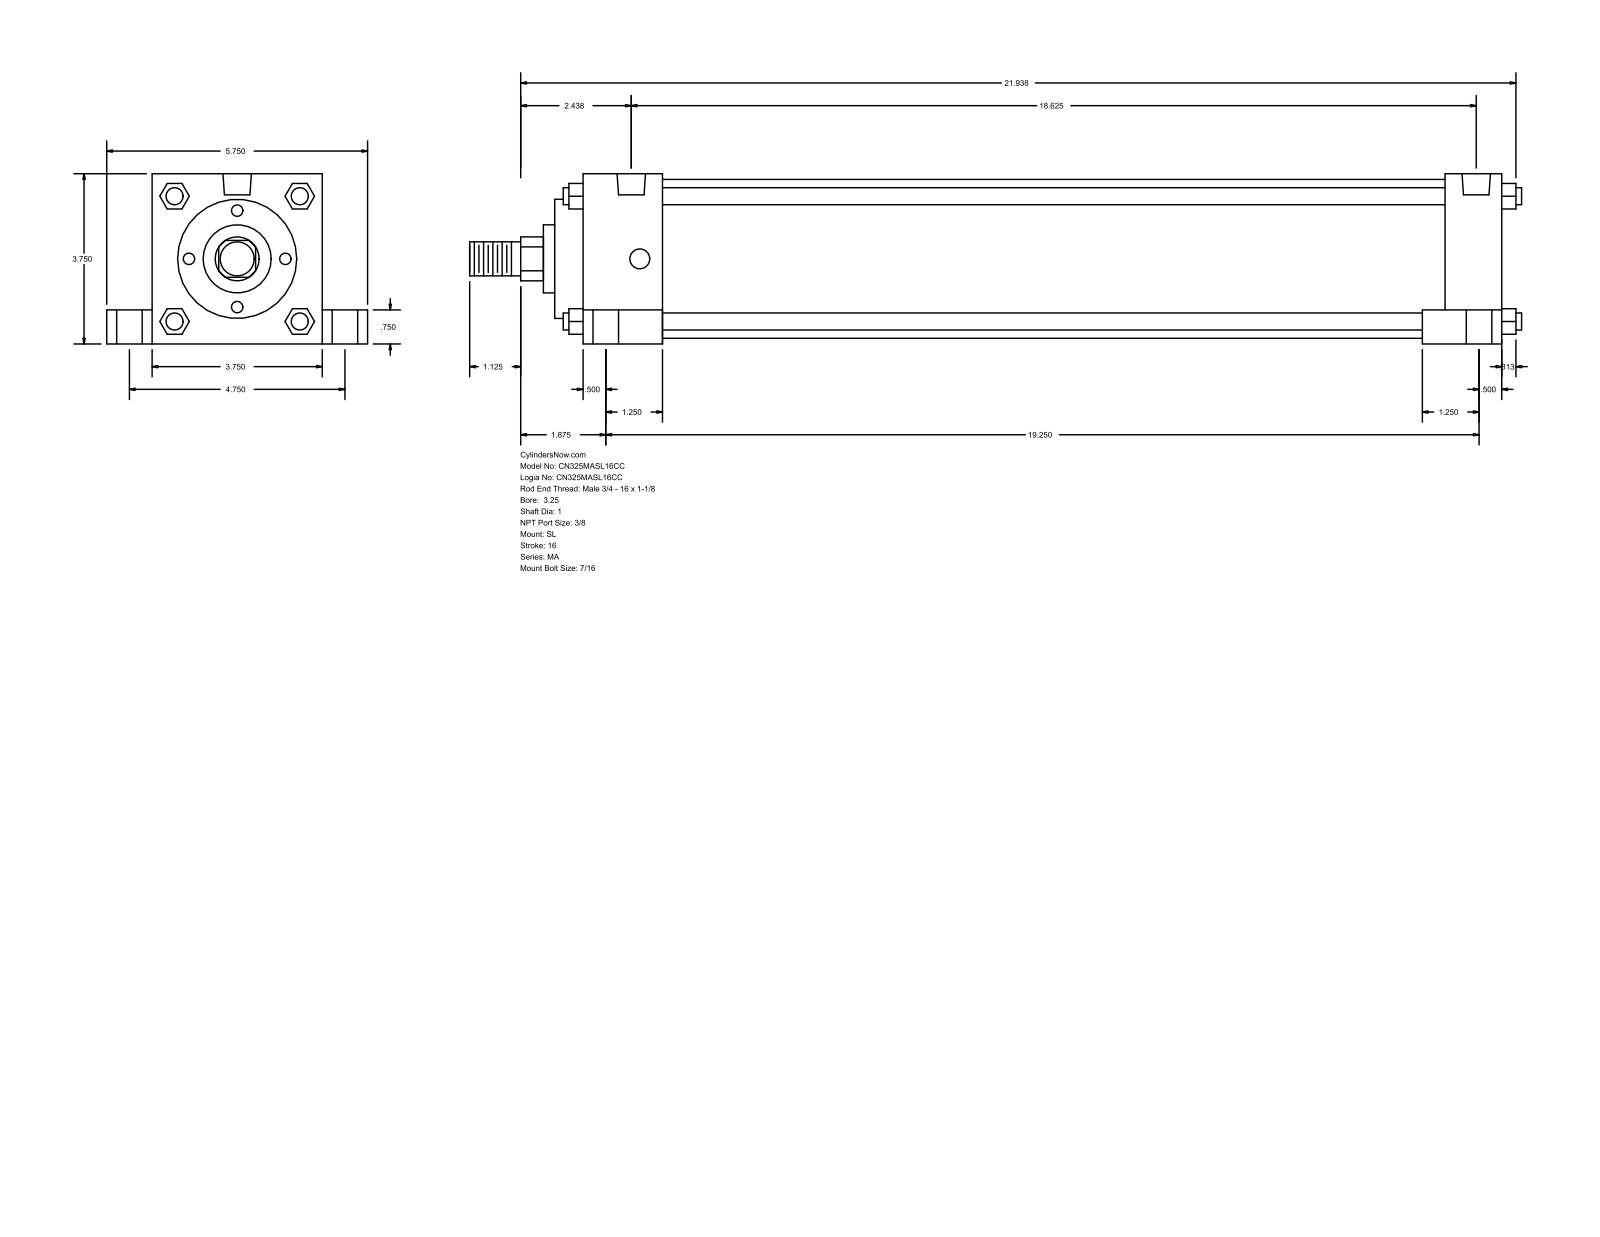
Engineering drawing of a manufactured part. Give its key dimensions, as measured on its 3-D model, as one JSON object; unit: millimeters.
{"part_name": "MA_SL__0325_1", "step_written_by": "GSSL Pune (CONFIG_CONTROL_DESIGN)", "units": "millimeters", "bodies": {"solids": 0, "faces": 150, "planar": 113, "cylindrical": 37, "other": 0}, "overall_size": [588.96, 146.05, 95.25], "round_holes": [[11.11, 4], [14.29, 4], [20.64, 4], [15.93, 2]], "round_bosses_or_shafts": [[9.53, 4], [88.9, 1], [66.67, 1], [38.1, 1], [25.4, 1], [19.05, 1]], "partial_cylinders_radius": [[12.29, 1]], "face_to_face_distances": [95.24, 514.35, 15.87, 25.41, 120.65, 530.22, 19.05, 482.6, 31.75, 44.46], "hole_center_spacings": [4.76, 60.35, 60.66, 62, 63.27, 120.66, 463.56, 468.32]}
